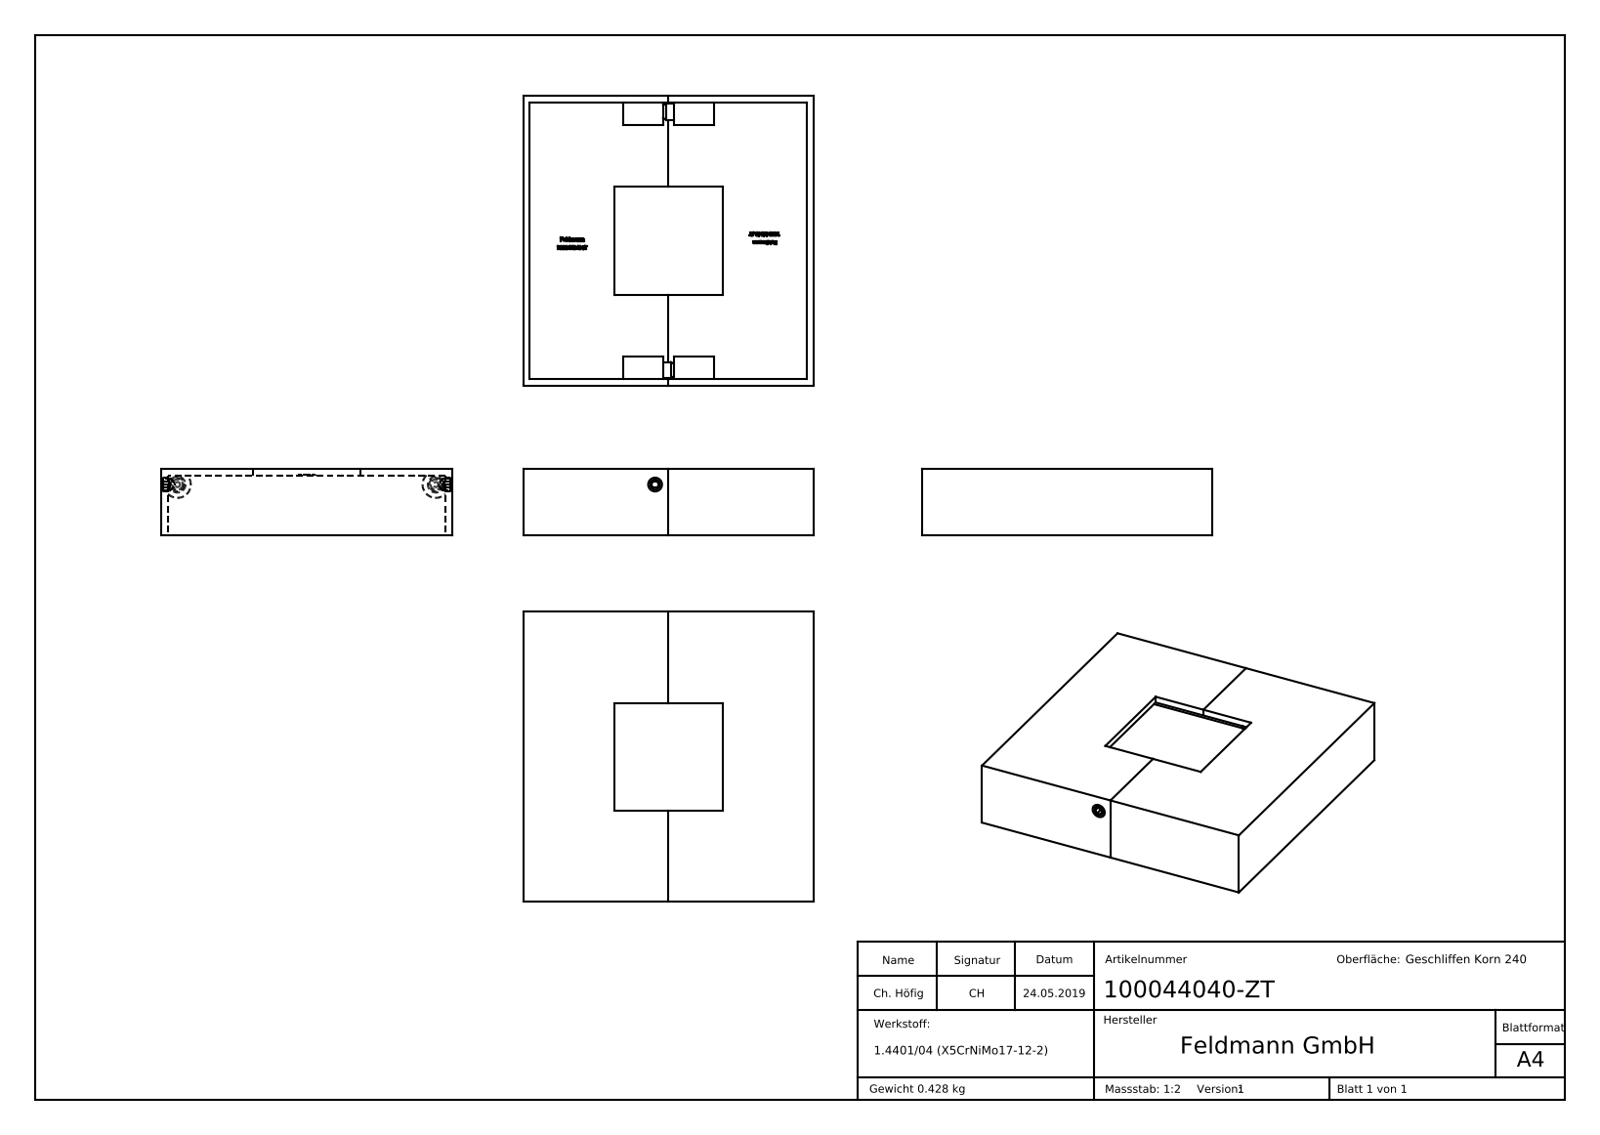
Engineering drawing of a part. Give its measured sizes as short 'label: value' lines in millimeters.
name: 100044040-ZT Teil2_100044040-ZT Teil2; DIN914_DIN 914 M5x5; 100044040-ZT; 100044040-ZT Teil1_100044040-ZT Teil1
written by: SolidWorks 2015 (CONFIG_CONTROL_DESIGN)
unit: mm
bodies: 6 solids, 612 faces (360 planar, 30 cylindrical, 222 other)
size: 109 × 109 × 25
volume: 53 544 mm³; area: 44 183 mm²
holes: 2× ⌀4.2, 2× ⌀5
bosses: 2× ⌀6, 2× ⌀5
rounds: 2× R5
face distances: 2.5, 106.5, 109, 104, 54.5, 52, 22.5, 25, 34.25, 74.75
hole spacings: 10, 97
